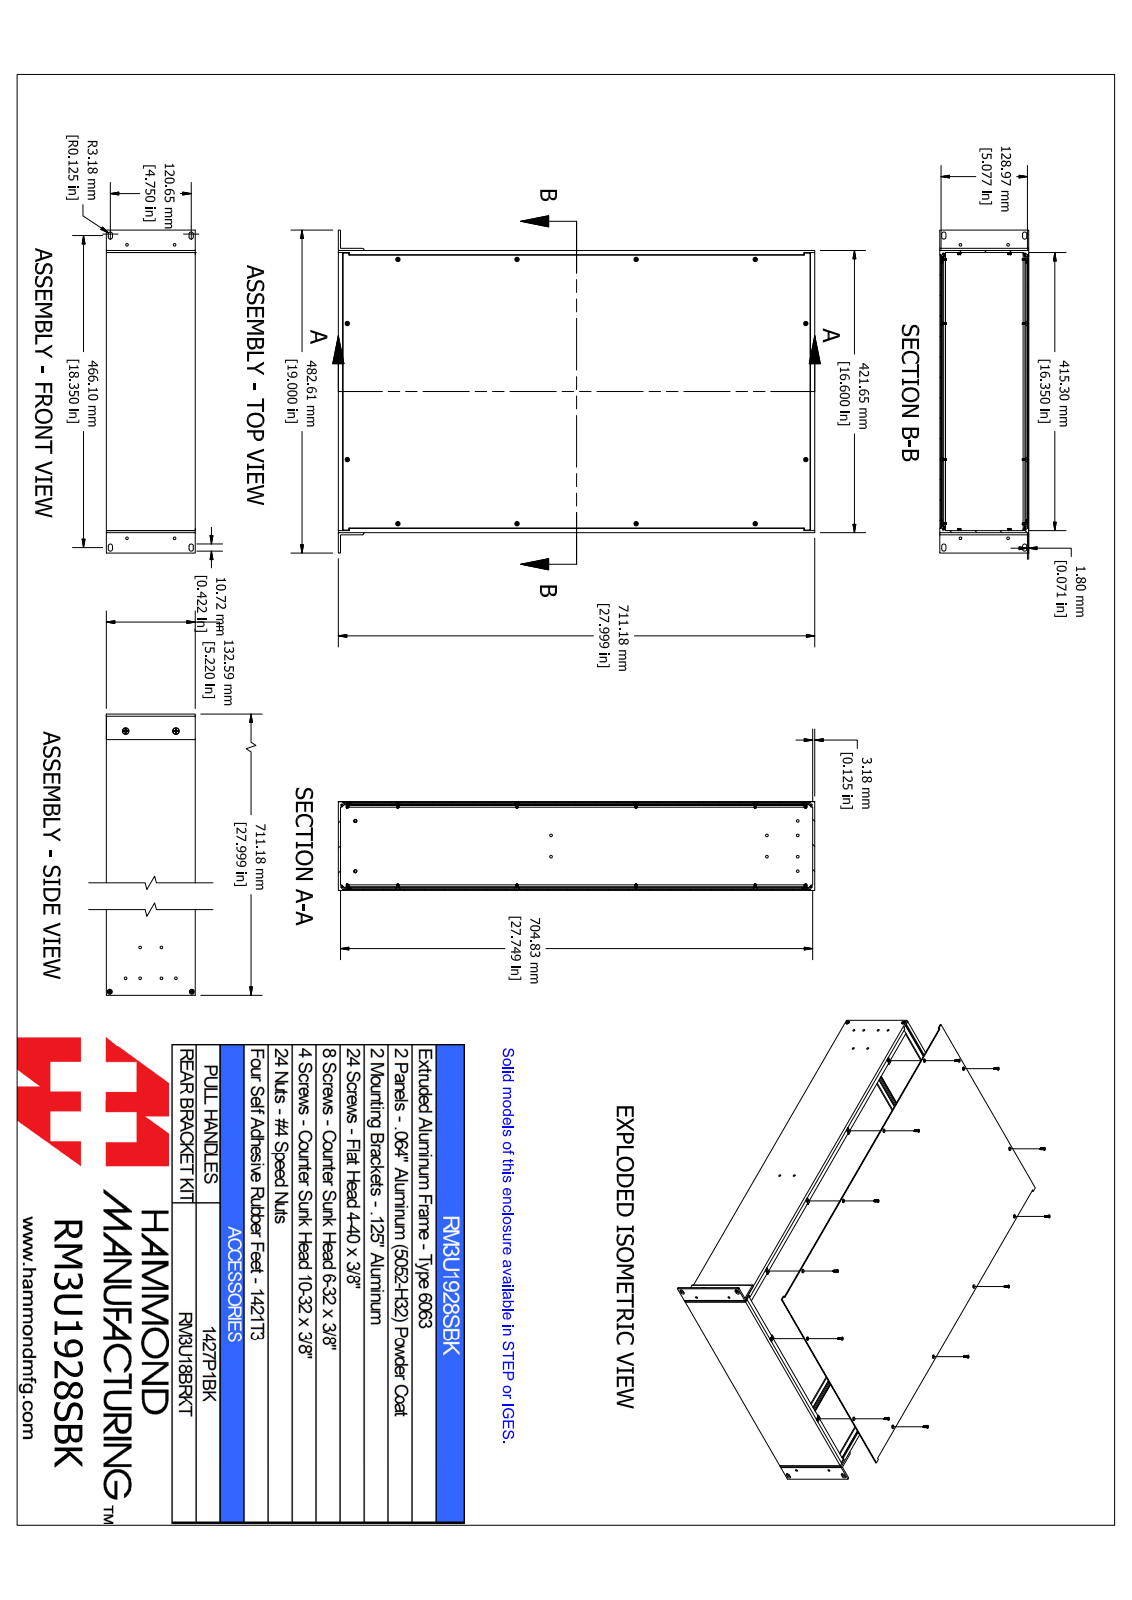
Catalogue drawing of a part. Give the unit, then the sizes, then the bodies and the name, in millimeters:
Units: millimetres
Overall size (bounding box): 711.2 × 482.6 × 132.6
Round holes (diameter × count): ⌀4 ×17, ⌀4.1 ×12, ⌀4.2 ×8, ⌀4 ×6, ⌀4 ×4, ⌀4 ×4, ⌀4.3 ×4, ⌀5 ×2
Round bosses / shafts (diameter × count): ⌀5.1 ×12, ⌀2.8 ×12, ⌀6 ×4, ⌀3.5 ×4, ⌀9.1 ×2, ⌀4.8 ×2
Partial cylindrical surfaces — rounded edges, fillets, slot ends (radius × count): R0.3 ×92, R0.6 ×92, R0.2 ×46, R0.4 ×46, R1 ×18, R0.4 ×16, R1 ×16, R0.9 ×12
Main face-to-face distances: 130.8, 1.8, 132.6, 129, 3.2, 418.5, 421.7, 415.3, 3.2, 711.2
Hole centre spacings: 177.8, 433, 355.6, 531.4, 678.4, 122, 203.2, 270.8
Volume: 2 214 000 mm³ · Surface area: 1 946 000 mm²
Bodies: 67 solids, 2579 faces (1064 planar, 611 cylindrical, 904 other)
Part name (STEP PRODUCT): RM3U1928SBK
STEP written by: SolidWorks 2021 (AUTOMOTIVE_DESIGN)
